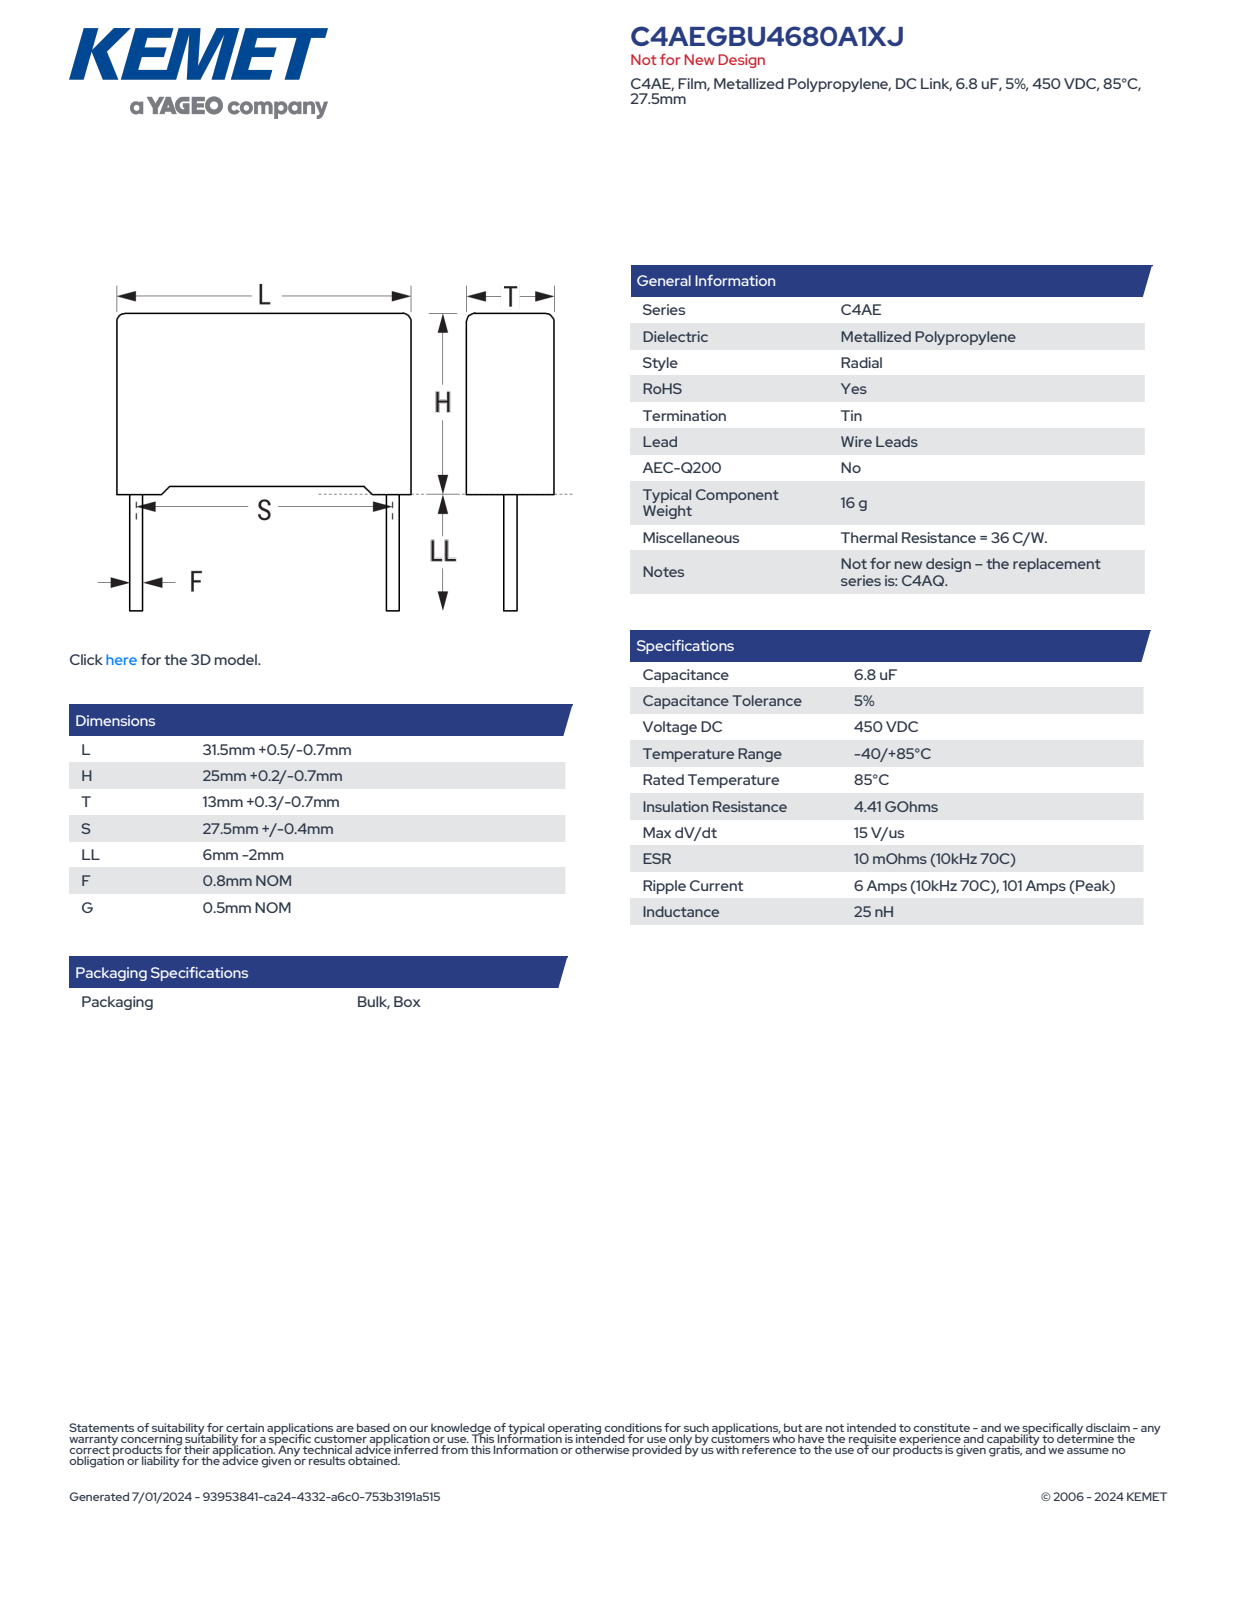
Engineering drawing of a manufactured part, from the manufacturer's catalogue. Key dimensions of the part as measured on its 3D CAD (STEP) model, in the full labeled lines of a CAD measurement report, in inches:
Part name (STEP PRODUCT): CFR_RB2CFP_31.5X25X13_L32H25.2T13.3S27.5LL4F0.8
STEP written by: SolidWorks 2014 (AUTOMOTIVE_DESIGN)
Units: inches
Bodies: 4 solids, 85 faces (77 planar, 8 cylindrical, 0 other)
Overall size (bounding box): 1.26 × 1.15 × 0.524
Volume: 0.635 in³ · Surface area: 4.965 in²
Round bosses / shafts (diameter × count): ⌀0.031 ×2
Partial cylindrical surfaces — rounded edges, fillets, slot ends (radius × count): R0.02 ×4
Main face-to-face distances: 0.524, 1.26, 0.958, 0.963, 0.034, 0.03, 0.992, 0.042, 0.524, 1.218
